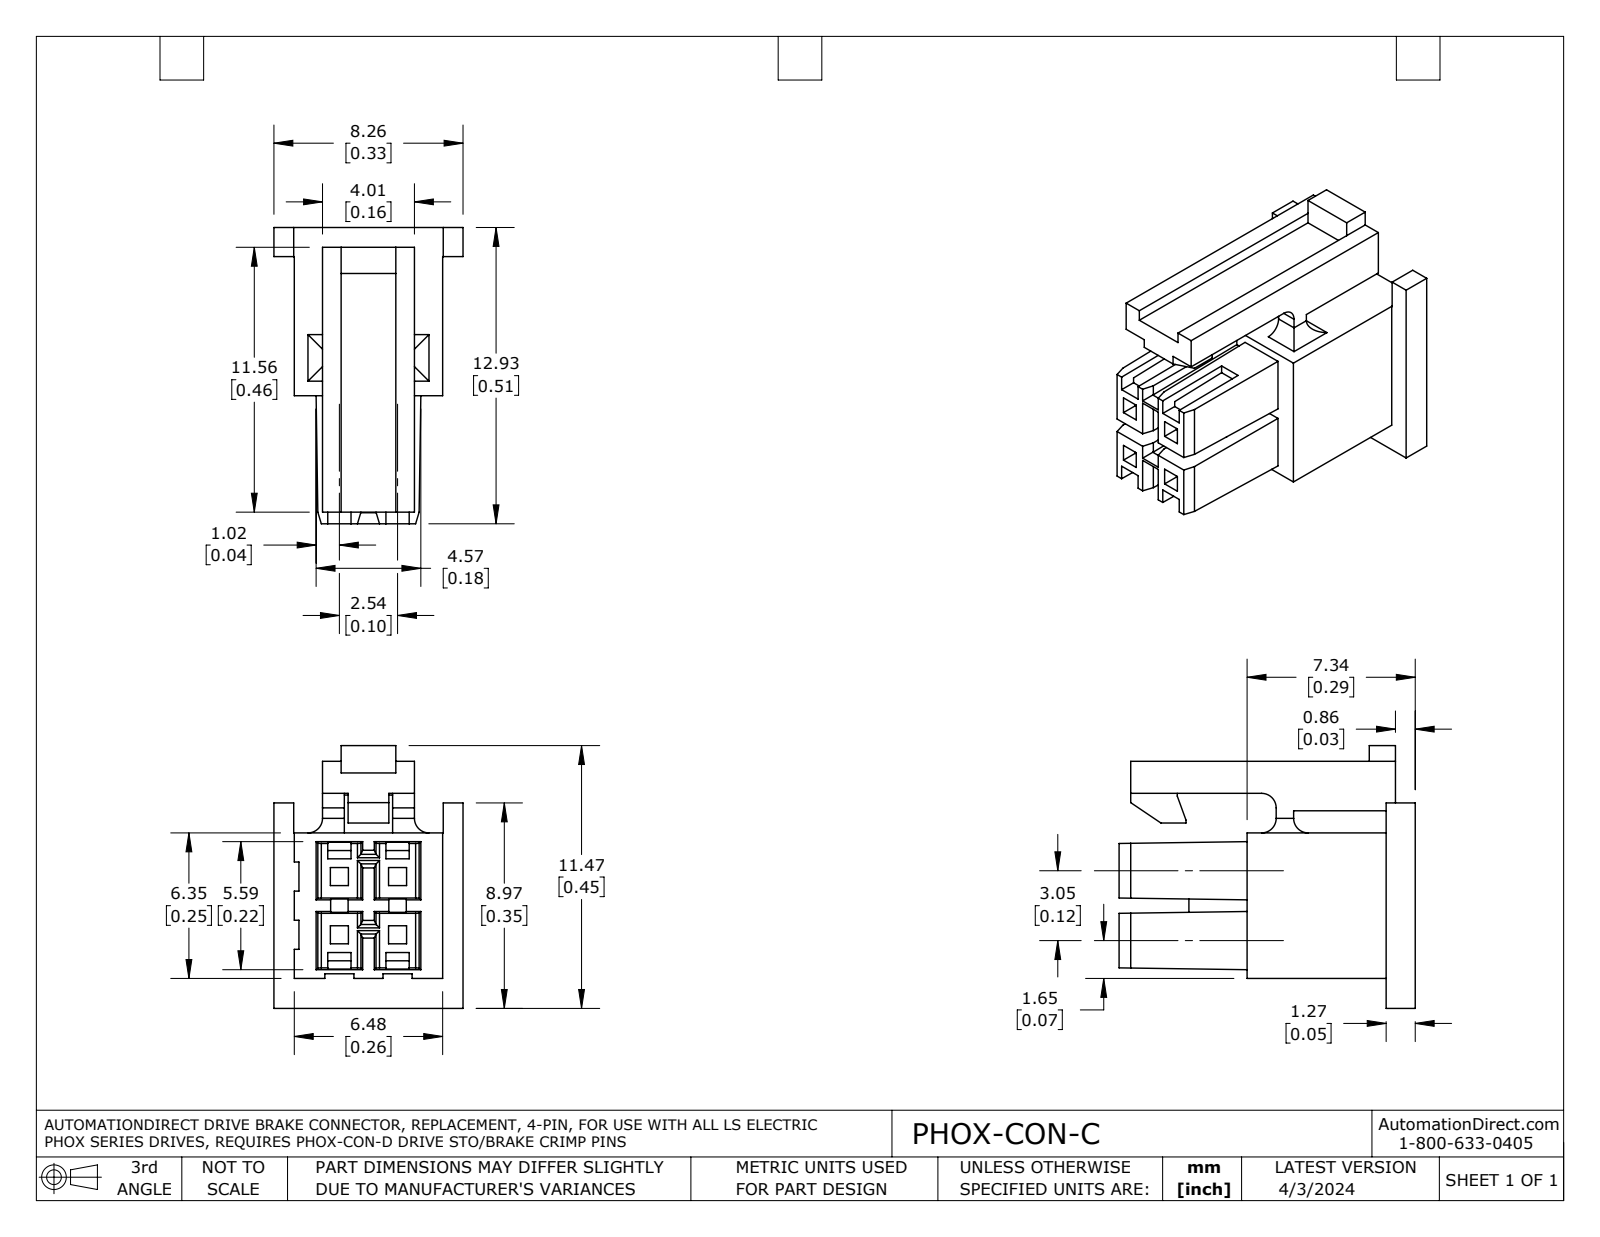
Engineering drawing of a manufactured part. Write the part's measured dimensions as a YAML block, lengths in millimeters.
part_name: "PHOX-CON-C"
step_written_by: "SolidWorks 2021 (AUTOMOTIVE_DESIGN)"
units: millimeters
bodies: {solids: 1, faces: 214, planar: 206, cylindrical: 8, other: 0}
overall_size: [12.9, 11.5, 8.3]
volume: 330
surface_area: 1074
partial_cylinders:
  - {radius: 0.6, count: 5}
face_to_face_distances: [2.5, 2.6, 3, 0.9, 6.5, 5.6, 1.7, 2.7, 5.3, 2]
